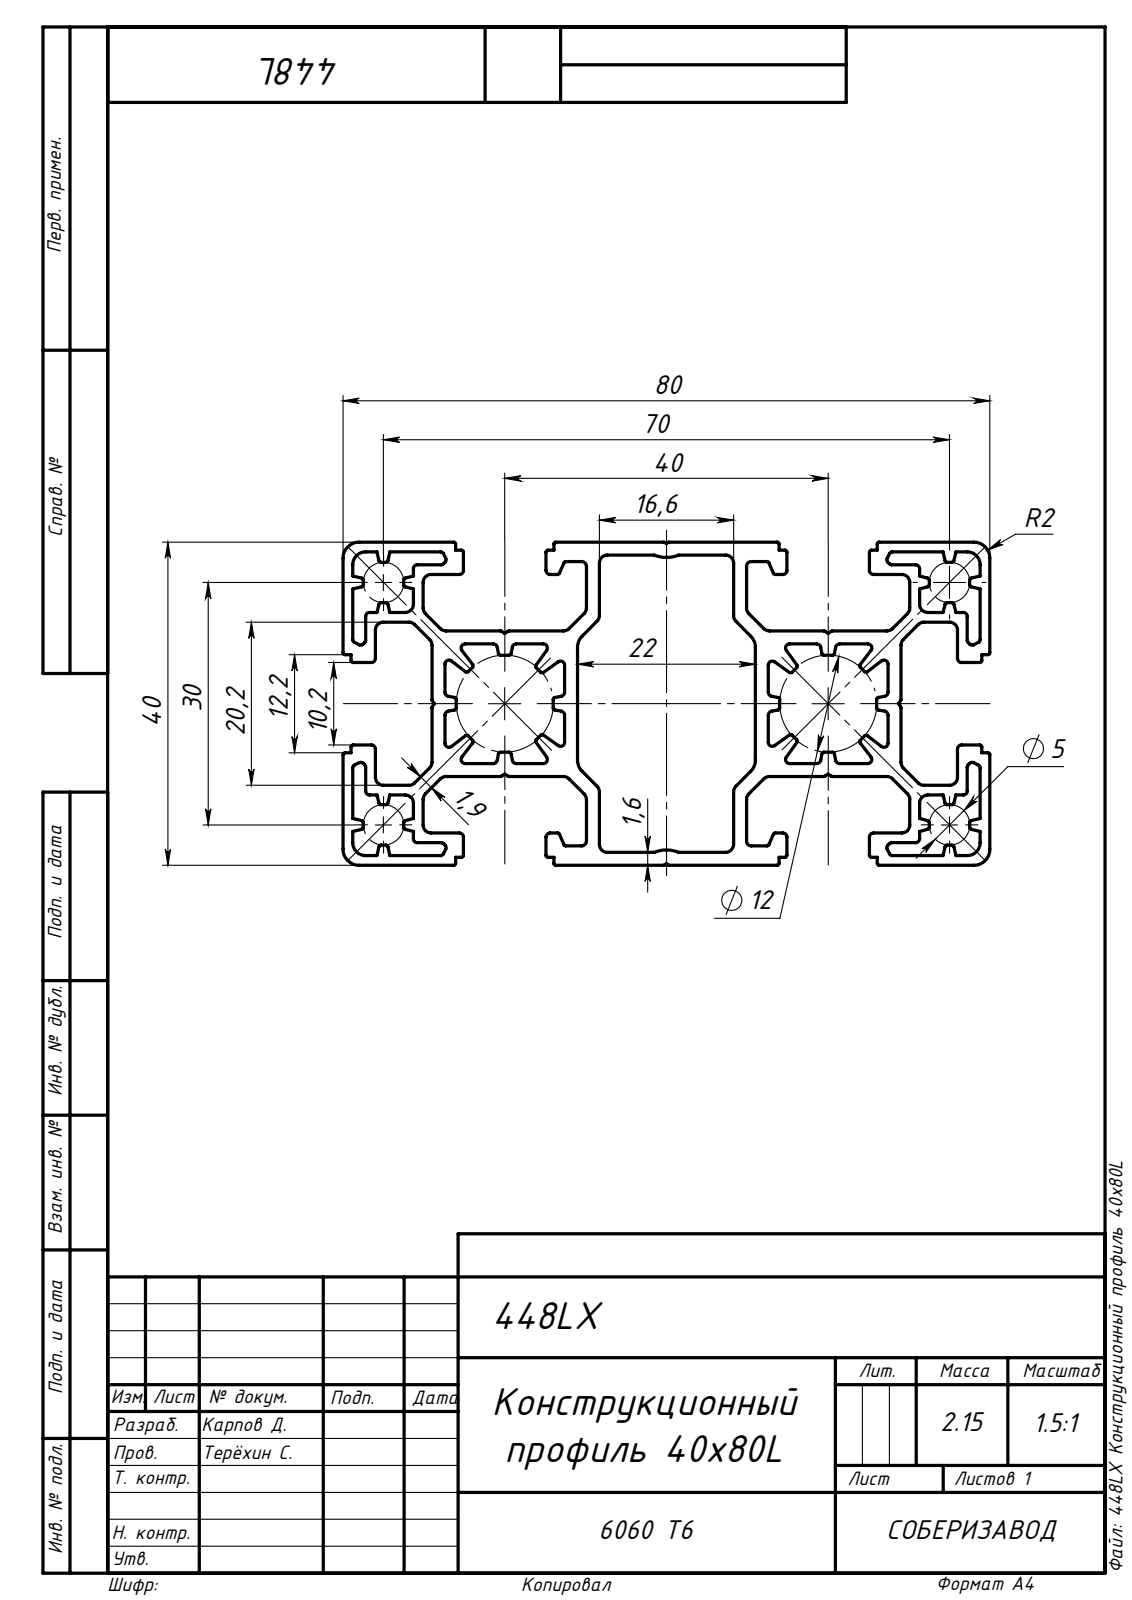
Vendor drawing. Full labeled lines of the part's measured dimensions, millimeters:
STEP written by: SolidWorks 2019 (AUTOMOTIVE_DESIGN)
Units: millimetres
Bodies: 1 solid, 578 faces (304 planar, 274 cylindrical, 0 other)
Overall size (bounding box): 1000 × 80 × 40
Volume: 797 237 mm³ · Surface area: 943 837 mm²
Partial cylindrical surfaces — rounded edges, fillets, slot ends (radius × count): R0.25 ×112, R0.5 ×52, R1 ×44, R0.4 ×24, R2 ×8, R0.6 ×4, R1.6 ×4, R4 ×2
Main face-to-face distances: 1.6, 40, 11, 1.2, 29, 9.8, 2.7, 27.4, 16.4, 19.1
